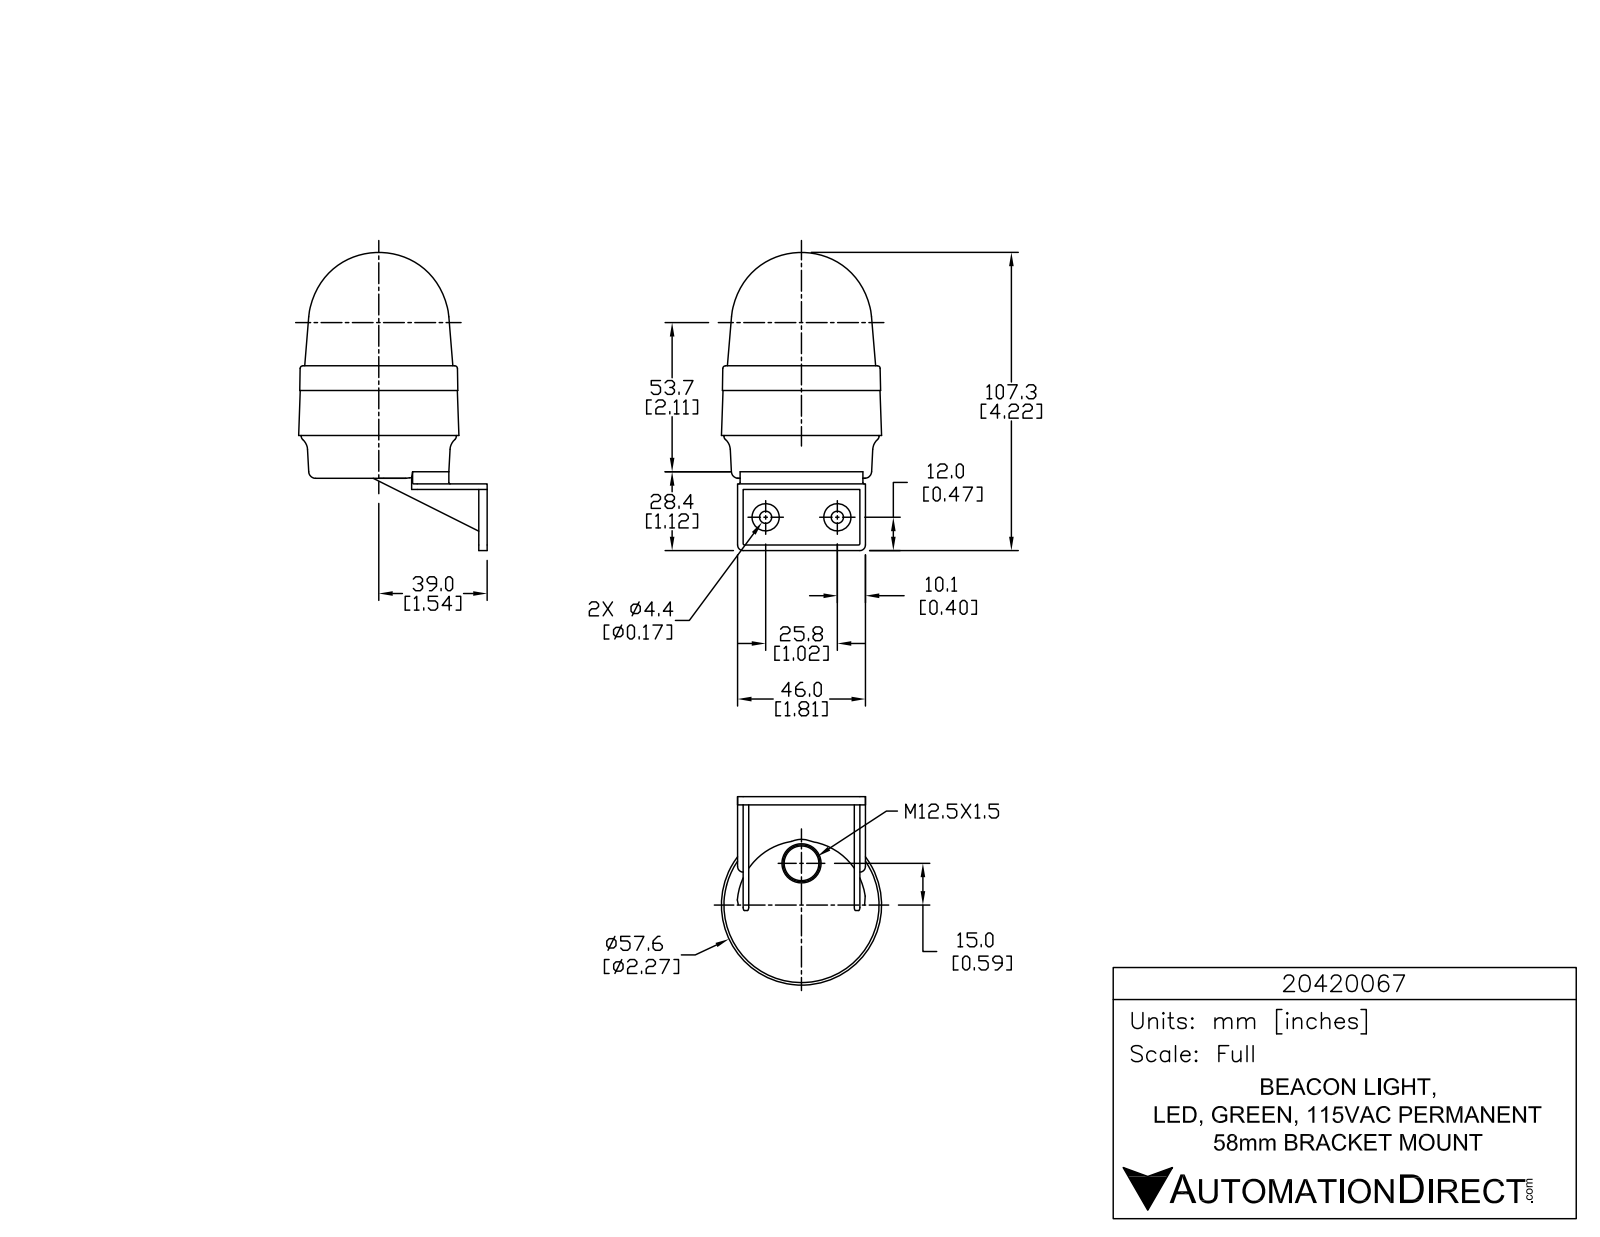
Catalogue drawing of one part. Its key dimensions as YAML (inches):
part_name: "20420067"
step_written_by: "SolidWorks 2015 (AUTOMOTIVE_DESIGN)"
units: inches
bodies: {solids: 1, faces: 828, planar: 551, cylindrical: 179, other: 98}
overall_size: [4.225, 2.852, 2.407]
volume: 10.27
surface_area: 33.38
round_holes:
  - {diameter: 0.039, count: 3}
  - {diameter: 0.173, count: 2}
round_bosses_or_shafts:
  - {diameter: 0.226, count: 3}
  - {diameter: 0.056, count: 3}
  - {diameter: 0.386, count: 2}
  - {diameter: 2.197, count: 1}
partial_cylinders:
  - {radius: 0.008, count: 6}
  - {radius: 0.008, count: 6}
  - {radius: 0.008, count: 6}
  - {radius: 0.02, count: 6}
  - {radius: 0.131, count: 6}
  - {radius: 0.079, count: 4}
  - {radius: 0.004, count: 3}
  - {radius: 0.005, count: 3}
face_to_face_distances: [0.079, 0.157, 1.575, 1.654, 0.039, 0.118, 1.496, 0.866, 0.945, 0.764]
hole_center_spacings: [1.016]
